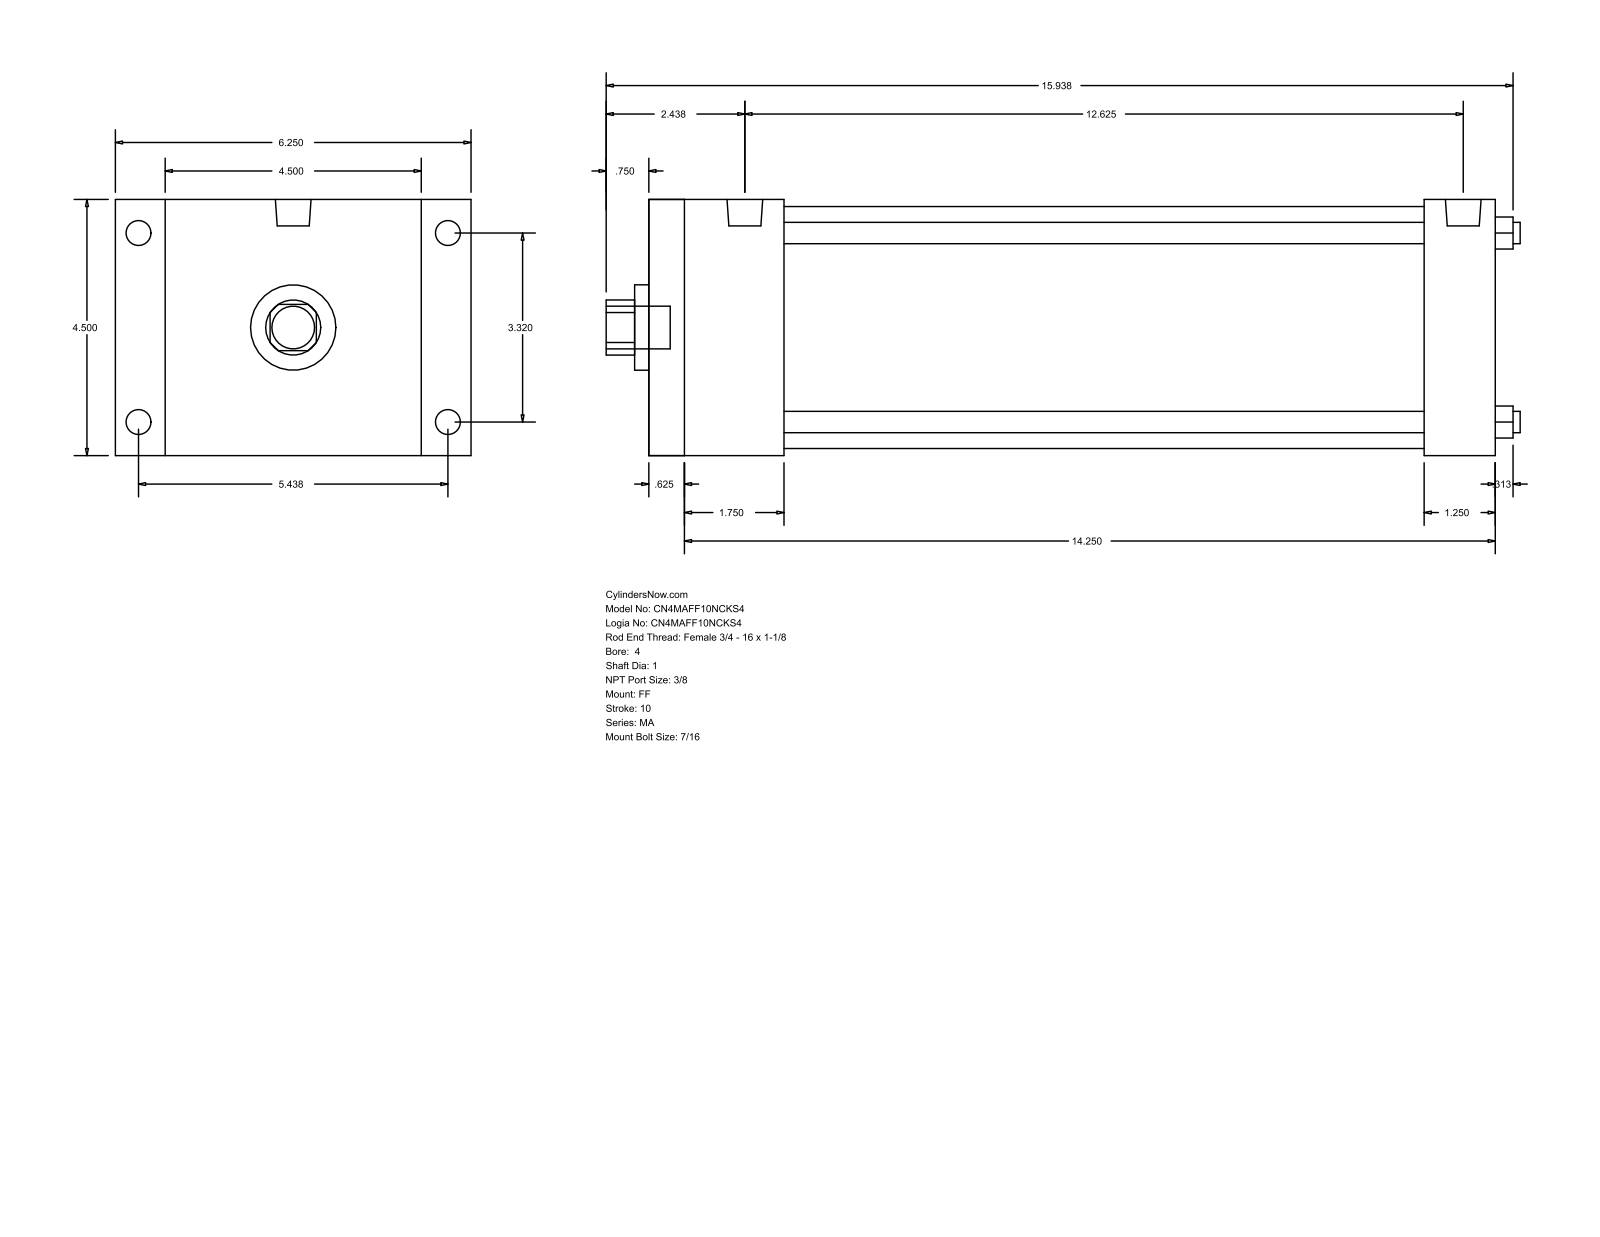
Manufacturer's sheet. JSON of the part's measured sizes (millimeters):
{"part_name": "MA_FF__0400_1", "step_written_by": "GSSL Pune (CONFIG_CONTROL_DESIGN)", "units": "millimeters", "bodies": {"solids": 0, "faces": 92, "planar": 64, "cylindrical": 28, "other": 0}, "overall_size": [407.99, 158.75, 114.3], "round_holes": [[9.53, 4], [25.4, 1], [38.1, 1], [107.95, 1]], "round_bosses_or_shafts": [[11.11, 8], [15.93, 2], [19.05, 1]], "partial_cylinders_radius": [[12.29, 1]], "face_to_face_distances": [114.3, 377.83, 15.87, 361.96, 22.23, 136.53, 346.07, 330.2, 31.76, 60.33], "hole_center_spacings": [59.62, 84.32, 119.25]}
